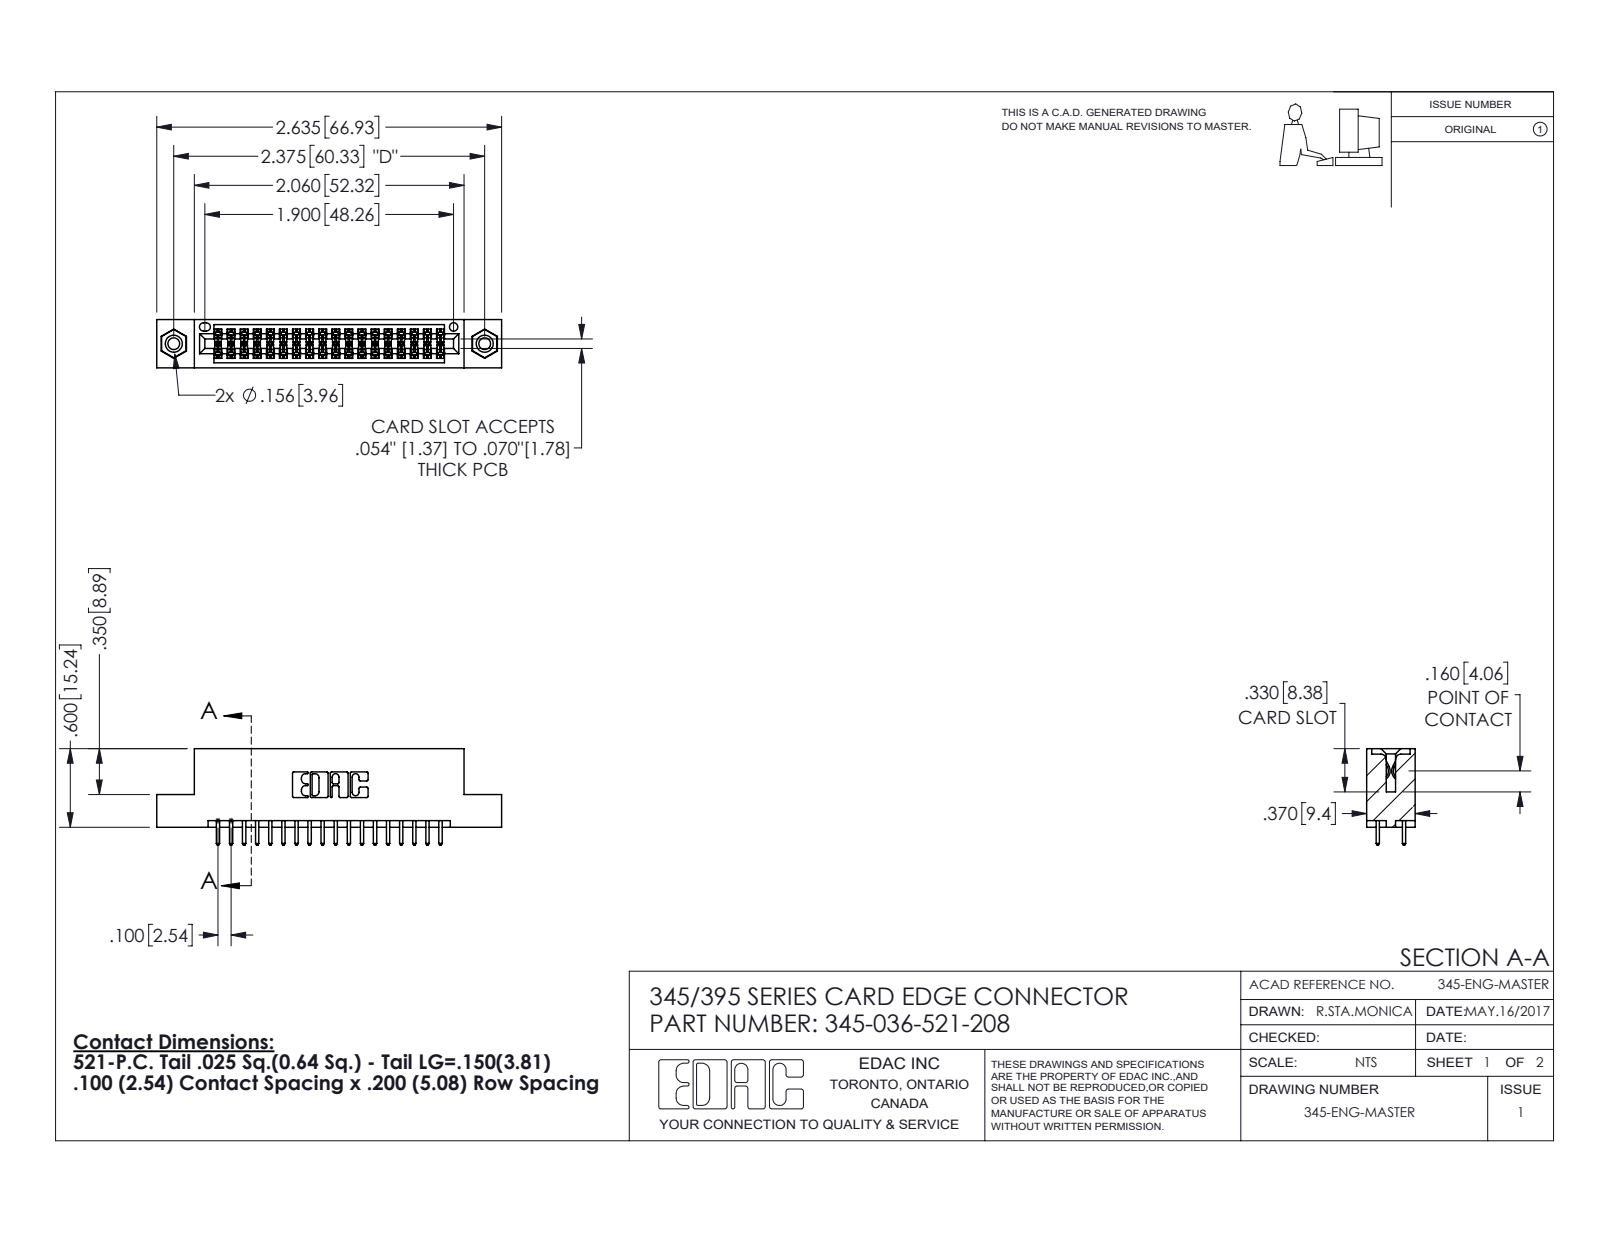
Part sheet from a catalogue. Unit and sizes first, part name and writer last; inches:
Units: inches
Overall size (bounding box): 2.635 × 0.737 × 0.37
Round holes (diameter × count): ⌀0.089 ×2, ⌀0.125 ×2, ⌀0.156 ×2, ⌀0.064 ×1
Round bosses / shafts (diameter × count): ⌀0.155 ×2
Partial cylindrical surfaces — rounded edges, fillets, slot ends (radius × count): R0.006 ×54, R0.01 ×36, R0.01 ×22, R0.007 ×6, R0.031 ×6, R0.026 ×3, R0.014 ×2, R0.019 ×2
Main face-to-face distances: 0.072, 0.298, 0.2, 0.37, 0.098, 0.272, 0.025, 0.225, 0.175, 0.1
Hole centre spacings: 0.27, 2.141, 2.375
Volume: 0.382 in³ · Surface area: 13.49 in²
Bodies: 39 solids, 1986 faces (1300 planar, 670 cylindrical, 16 other)
Part name (STEP PRODUCT): 345-292-001_345-293-121; 345-250-001_345-250-003-102; 345 Part_Flush Mounting Lugs - 0.156 Dia-TI; 345-036-521-208
STEP written by: SolidWorks 2016 (CONFIG_CONTROL_DESIGN)
